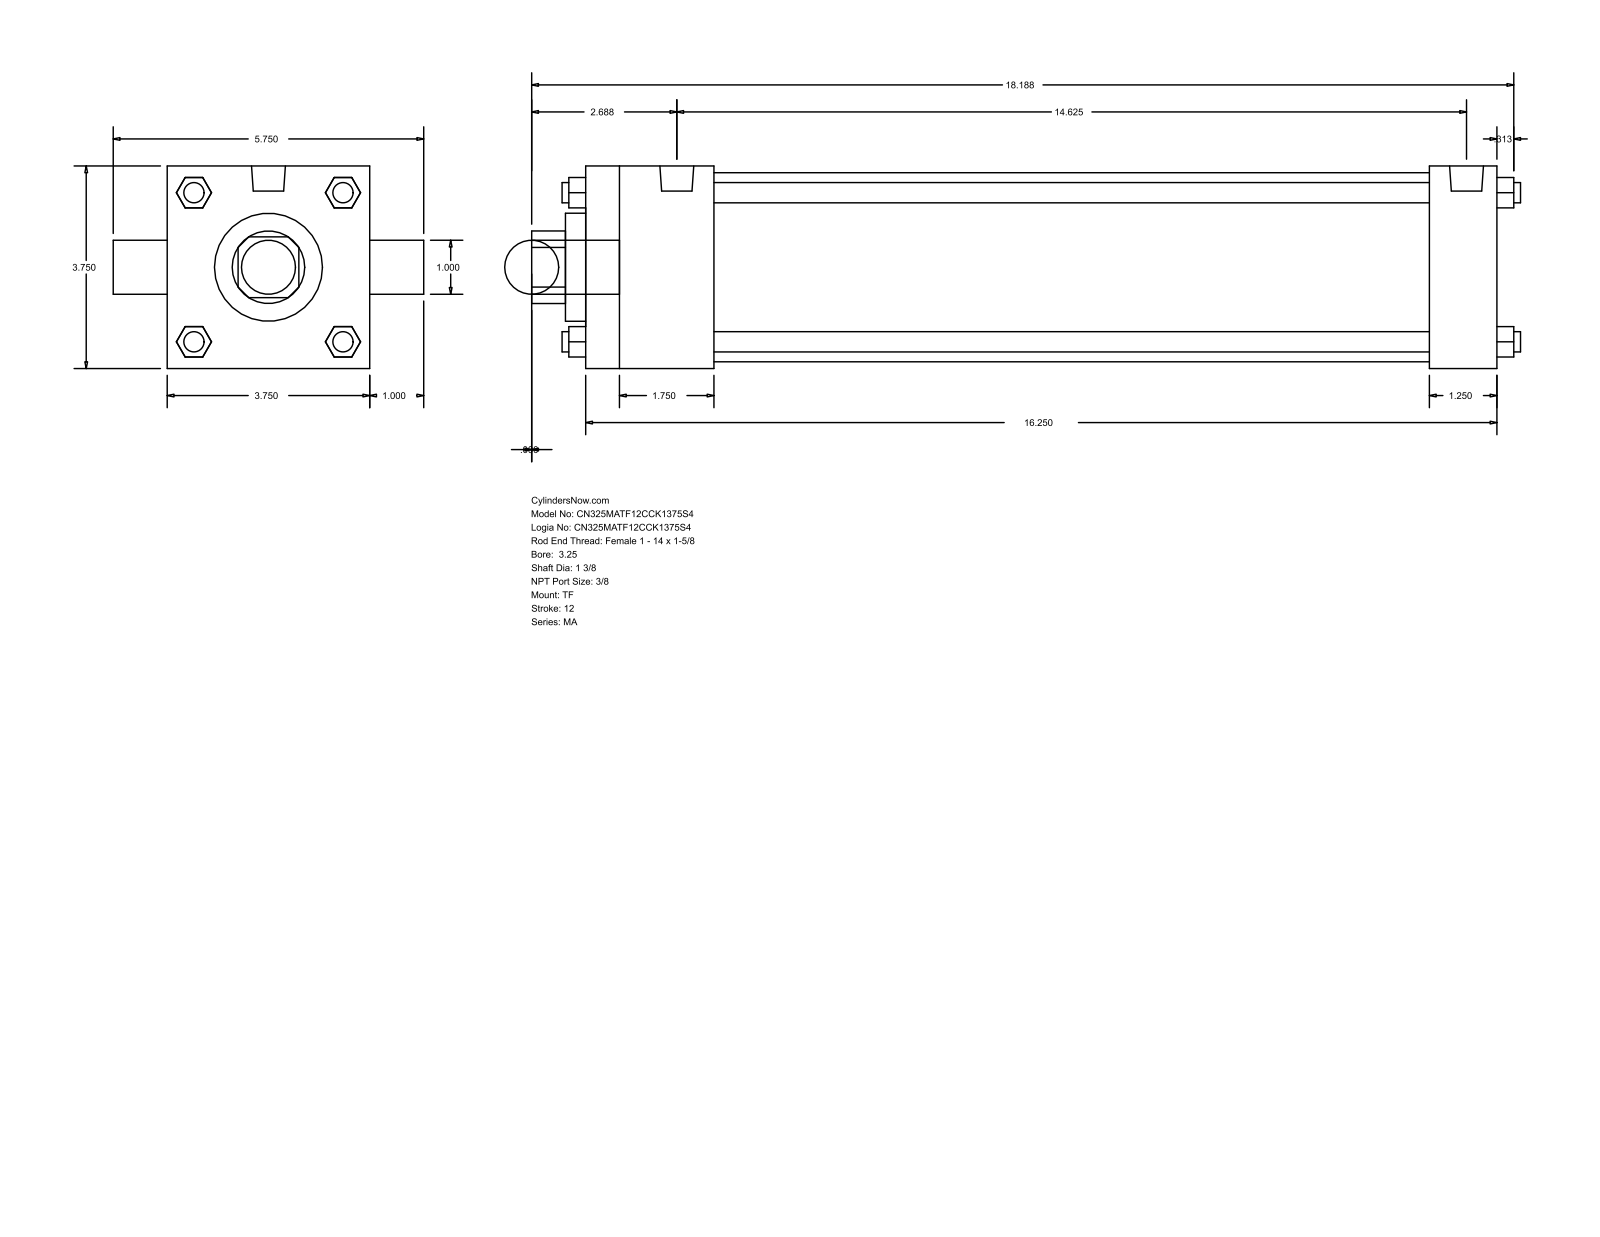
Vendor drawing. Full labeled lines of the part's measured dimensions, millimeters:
Part name (STEP PRODUCT): MA_TF__0325_1.375
STEP written by: GSSL Pune (CONFIG_CONTROL_DESIGN)
Units: millimetres
Bodies: 0 solids, 120 faces (92 planar, 28 cylindrical, 0 other)
Overall size (bounding box): 465.14 × 146.05 × 95.25
Round holes (diameter × count): ⌀25.4 ×1, ⌀34.92 ×1, ⌀50.8 ×1, ⌀88.9 ×1
Round bosses / shafts (diameter × count): ⌀9.53 ×4, ⌀11.11 ×3, ⌀15.93 ×2, ⌀25.4 ×1
Partial cylindrical surfaces — rounded edges, fillets, slot ends (radius × count): R17.06 ×1
Main face-to-face distances: 95.24, 428.62, 60.32, 396.87, 336.55, 368.3, 31.75, 9.52, 69.84, 406.39
